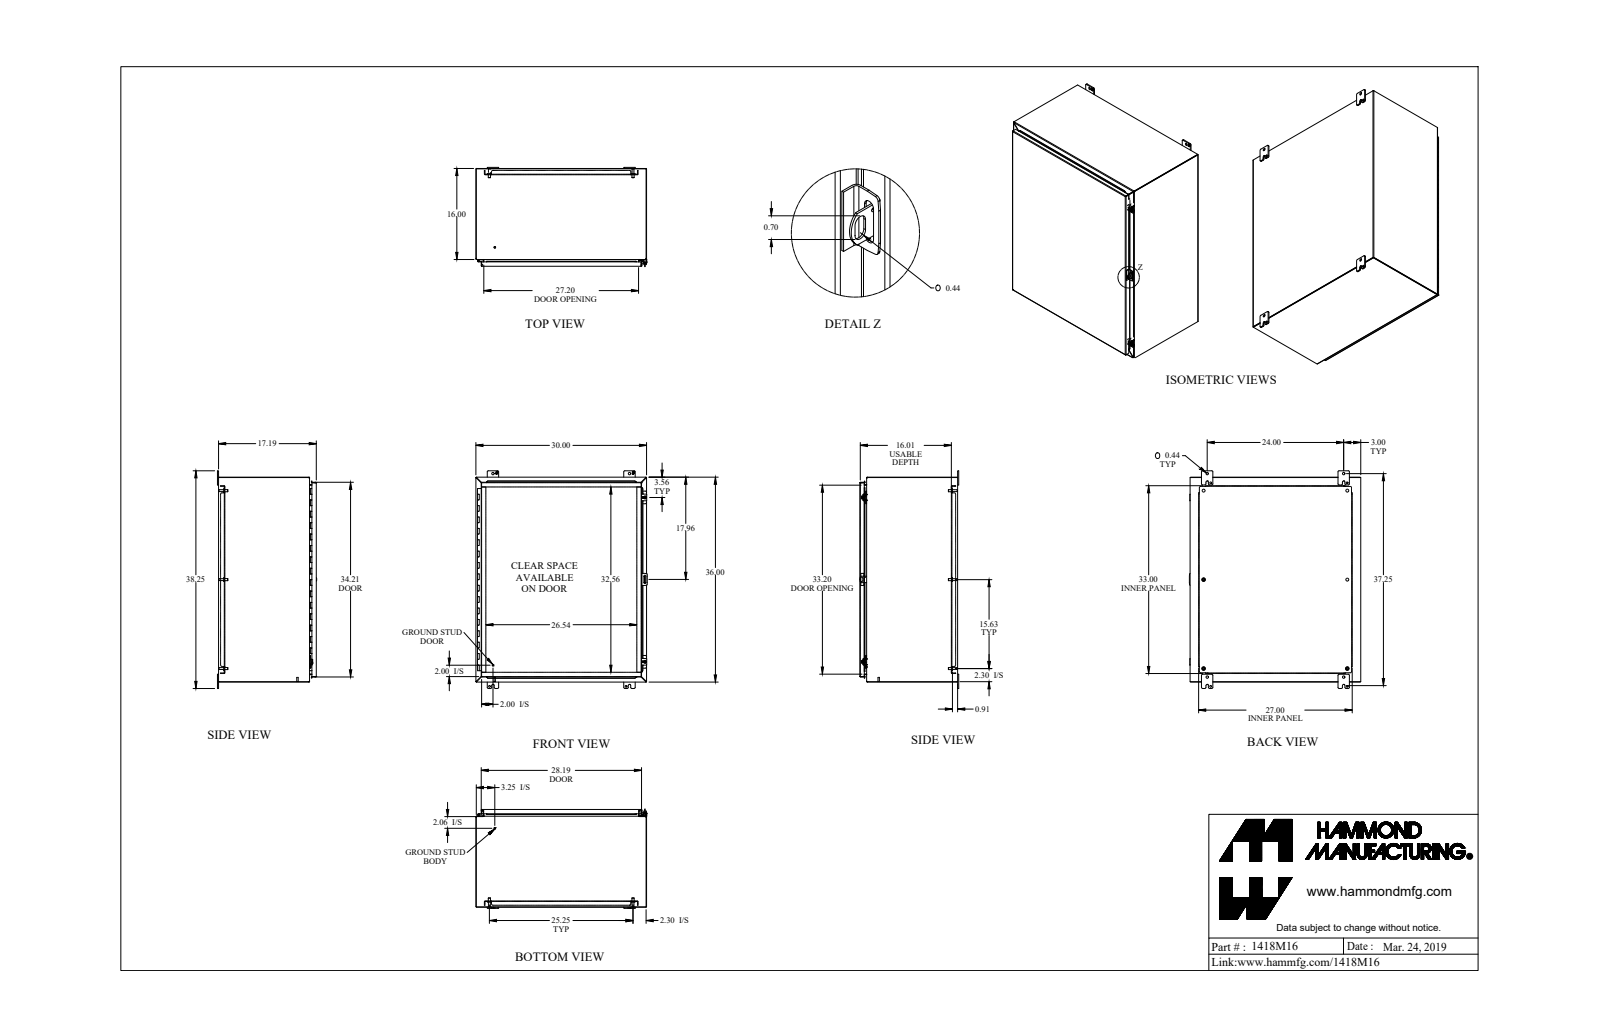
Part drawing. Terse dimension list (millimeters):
name: 1418M16_Default
written by: SolidWorks 2019 (CONFIG_CONTROL_DESIGN)
unit: mm
bodies: 49 solids, 1431 faces (837 planar, 502 cylindrical, 92 other)
size: 971.6 × 765.2 × 442.9
volume: 7 584 000 mm³; area: 7 826 000 mm²
holes: 6× ⌀12.7, 4× ⌀7.8, 4× ⌀8, 4× ⌀11.1, 4× ⌀11.3, 2× ⌀5.4, 2× ⌀6.7, 2× ⌀9.5, 1× ⌀3.2, 1× ⌀4.7
bosses: 6× ⌀16.5, 6× ⌀9.5, 6× ⌀8.4, 4× ⌀25.4, 2× ⌀12.7, 2× ⌀9.9, 2× ⌀7.1, 2× ⌀6.4
rounds: 36× R4.8, 22× R0.9, 22× R2.7, 20× R6.4, 13× R1.2, 13× R3.6, 12× R2.9, 8× R1
face distances: 1.8, 434.7, 432.8, 760.2, 436.5, 2.4, 912.6, 23.8, 25.6, 408.5
hole spacings: 641.4, 396.9, 609.6, 754.2, 1093.7, 696, 793.8, 793.8
